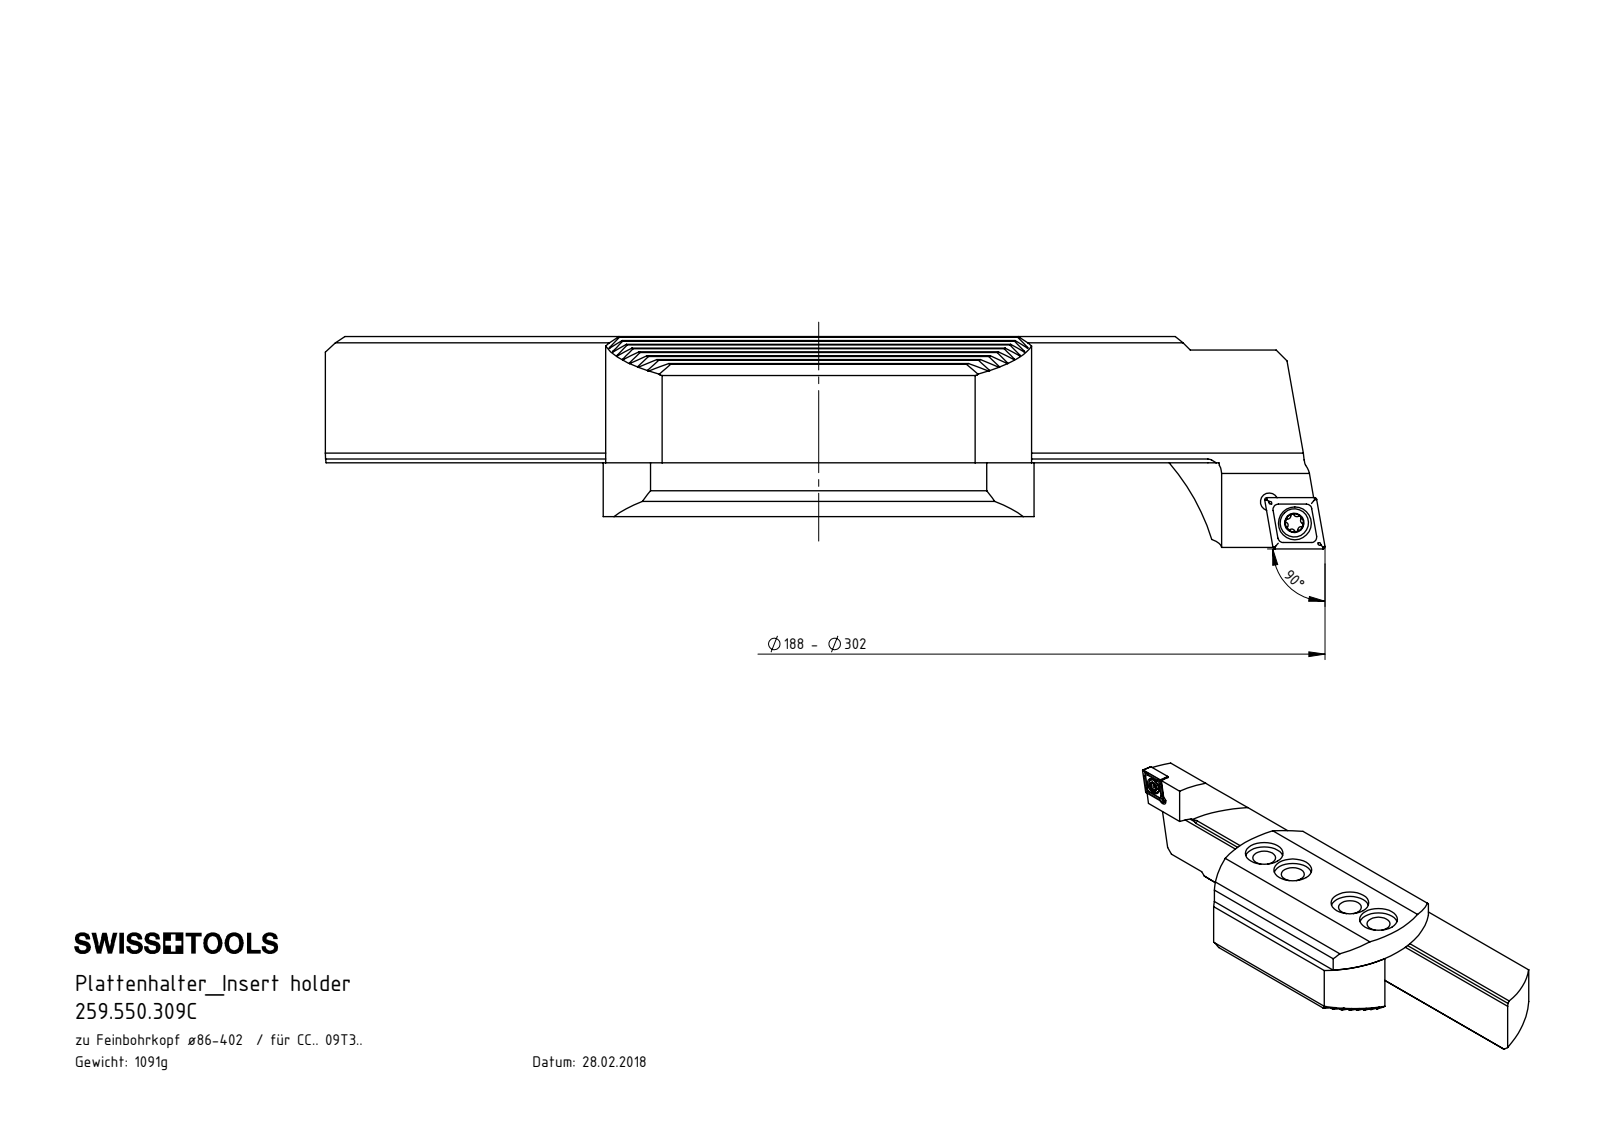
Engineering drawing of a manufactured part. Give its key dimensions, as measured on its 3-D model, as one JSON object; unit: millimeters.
{"part_name": "F00-WCB.136.003_A; 259.550.309C; F00-WCB.188.001_mit Wp; F00-WCB.136.002_A (+3 more)", "step_written_by": "SolidWorks 2017 (CONFIG_CONTROL_DESIGN)", "units": "millimeters", "bodies": {"solids": 5, "faces": 770, "planar": 462, "cylindrical": 67, "other": 241}, "overall_size": [185.57, 55, 39.4], "volume_mm3": 139002, "surface_area_mm2": 36711, "round_holes": [[8.5, 4], [14, 4], [3.3, 2], [4.4, 1], [6.1, 1]], "round_bosses_or_shafts": [[5.25, 1], [4, 1]], "partial_cylinders_radius": [[0.2, 16], [0.34, 6], [0.59, 6], [40, 6], [0.8, 1]], "face_to_face_distances": [2.38, 4.76, 21.3, 33.7, 7.14, 9.52, 12.4, 4.77, 7.15, 9.53], "hole_center_spacings": [15, 45, 6.06, 6.19, 30, 60]}
